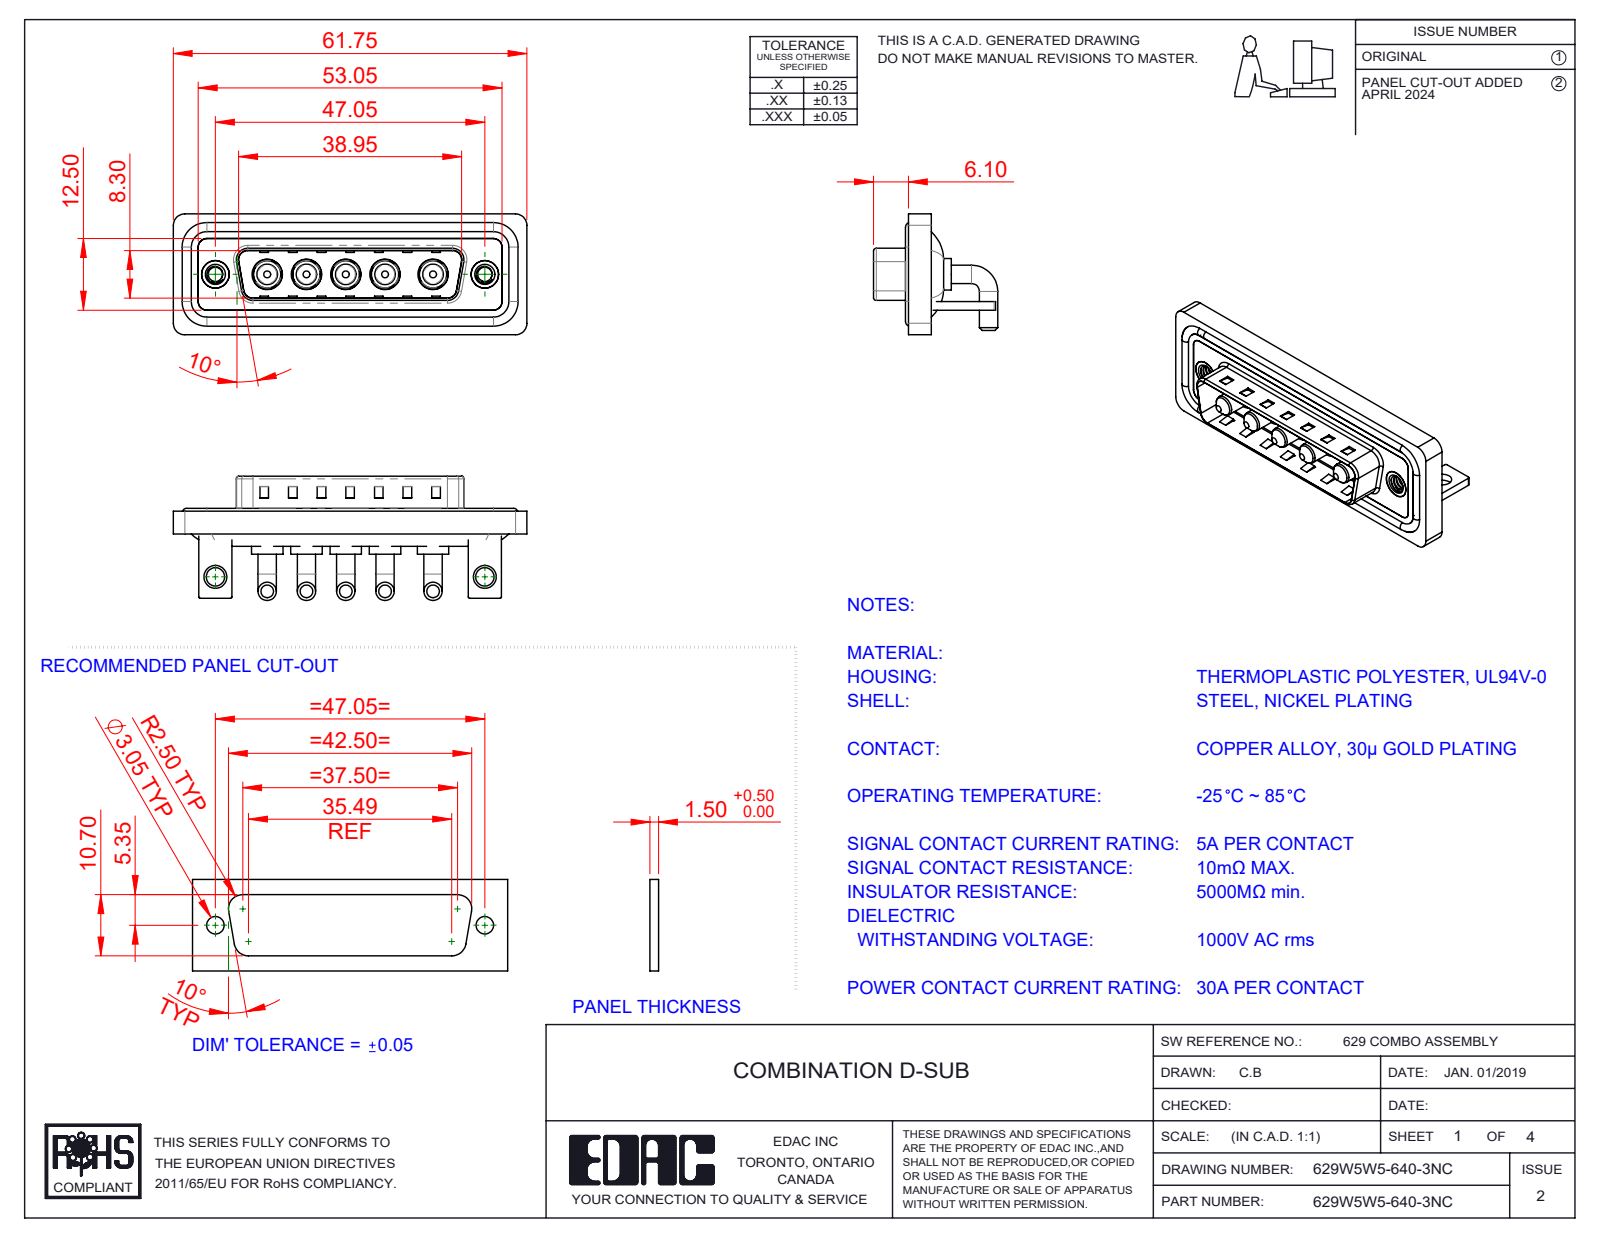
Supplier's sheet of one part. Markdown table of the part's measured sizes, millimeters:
| quantity | value |
| --- | --- |
| part name | 629W5W5-640-3NC; 629Combo Housing_5W5; 629Combo Threaded Rivet_B; Power Pin_30A RA (+4 more) |
| STEP written by | SolidWorks 2023 (CONFIG_CONTROL_DESIGN) |
| units | millimeters |
| bodies | 19 solids, 736 faces (279 planar, 311 cylindrical, 146 other) |
| overall size | 61.75 × 21.7 × 21.1 |
| volume | 8 214 mm³ |
| surface area | 12 952 mm² |
| round holes (diameter × count) | 4.85 × 5, 5.3 × 5, 2.5 × 2, 3.2 × 2, 4 × 2, 4.8 × 2, 5 × 2 |
| round bosses / shafts (diameter × count) | 3.2 × 10, 5.5 × 5, 5.2 × 5, 4.75 × 5, 3.75 × 5, 3.6 × 5, 1.6 × 4, 4.9 × 2 |
| partial cylindrical surfaces (radius × count) | 2 × 19, 1.5 × 18, 0.25 × 16, 0.5 × 9, 1.6 × 8, 2.1 × 5, 0.6 × 4, 0.65 × 4 |
| main face-to-face distances | 0.4, 1.5, 2.9, 0.8, 2.1, 3.7, 1.1, 4.5, 4.1, 1.2 |
| hole center spacings | 6.86, 13.73, 47.05, 6.85, 6.87, 8.37, 8.38, 9.04 |
